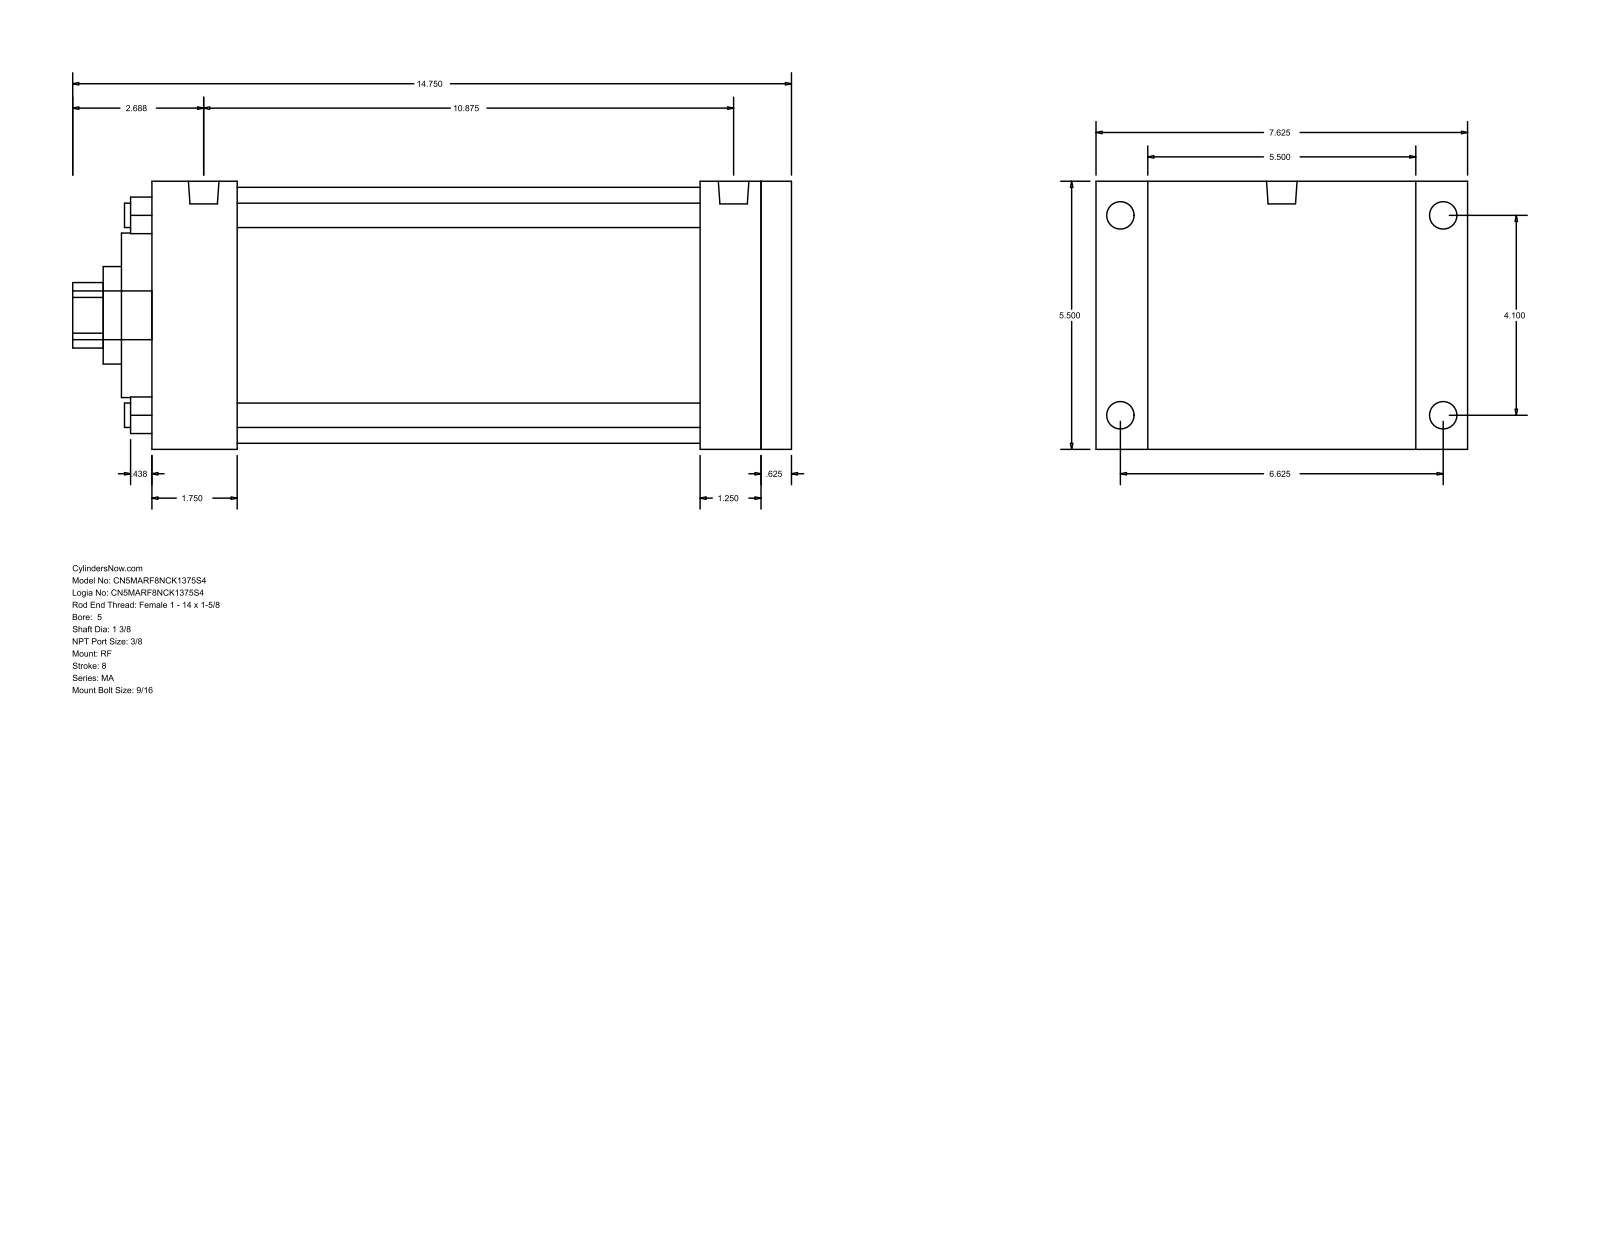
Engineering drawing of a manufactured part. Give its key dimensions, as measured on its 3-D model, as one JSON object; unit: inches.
{"part_name": "MA_RF__0500_1.375", "step_written_by": "GSSL Pune (CONFIG_CONTROL_DESIGN)", "units": "inches", "bodies": {"solids": 0, "faces": 94, "planar": 65, "cylindrical": 29, "other": 0}, "overall_size": [14.75, 7.625, 5.5], "round_holes": [[0.5, 4], [1.375, 1], [2, 1], [3.375, 1], [5.25, 1]], "round_bosses_or_shafts": [[0.563, 4], [0.437, 4], [0.627, 2], [1, 1]], "partial_cylinders_radius": [[0.672, 1]], "face_to_face_distances": [5.5, 13.125, 0.625, 12.5, 1.75, 10.75, 11.375, 11.25, 9.5, 1.25], "hole_center_spacings": [2.899, 4.1, 5.798]}
